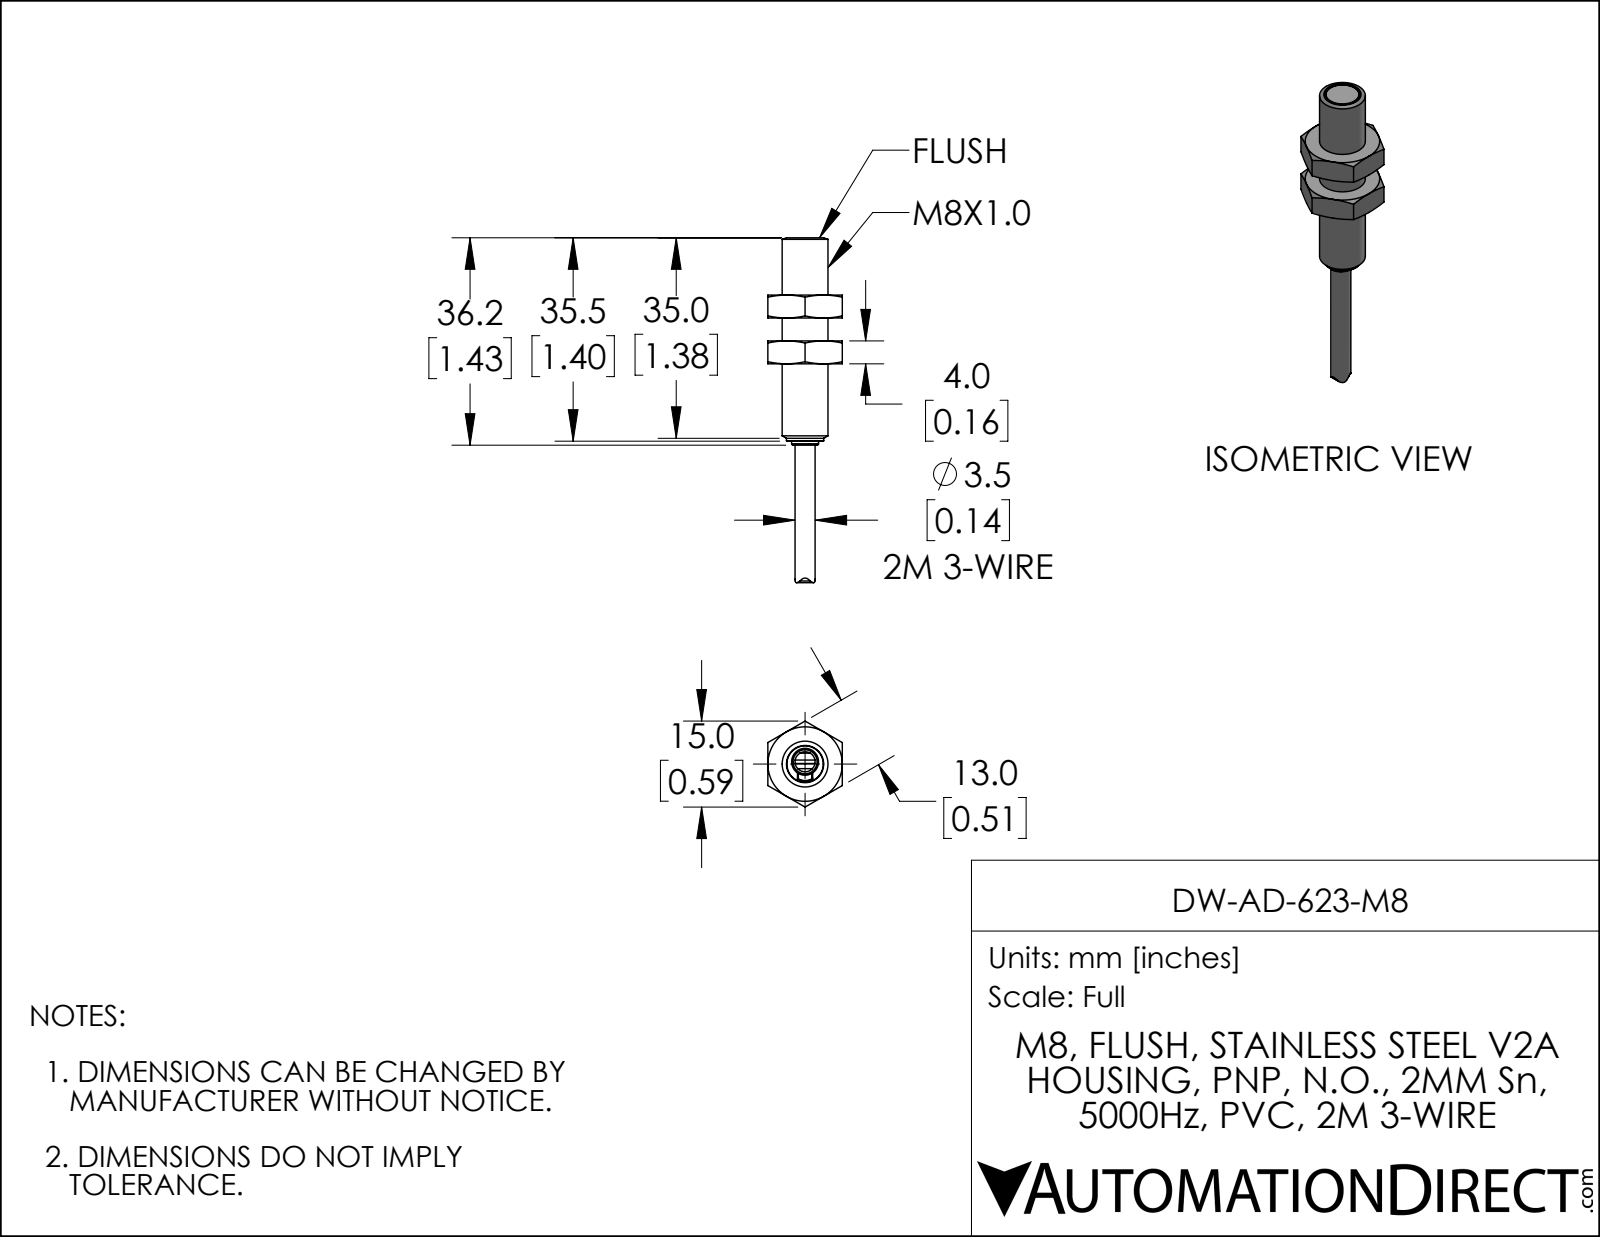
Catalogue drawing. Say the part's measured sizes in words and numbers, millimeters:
The part is named "DW-AD-623-M8". Its 3-D file was written by "SolidWorks 2019 (AUTOMOTIVE_DESIGN)". It is 1 solid with 79 faces: 24 planar, 18 cylindrical and 37 other. Overall it measures 60.2 by 15 by 13 millimeters. Its volume is 2 770 cubic millimeters and its surface area 1 773 square millimeters. Round bosses or shafts: 1 of diameter 8, 1 of diameter 6.5, 1 of diameter 4.7, 1 of diameter 3.5. Partial cylindrical surfaces (rounded edges, fillets, slot ends): 2 of radius 0.3, 1 of radius 0.6, 1 of radius 0.8, 1 of radius 2.9, 1 of radius 3, 1 of radius 4.5, 1 of radius 6. The main face-to-face distances are 4, 13, 8, 12, 10, 14, 18, 22, 35.5, 25.5.
